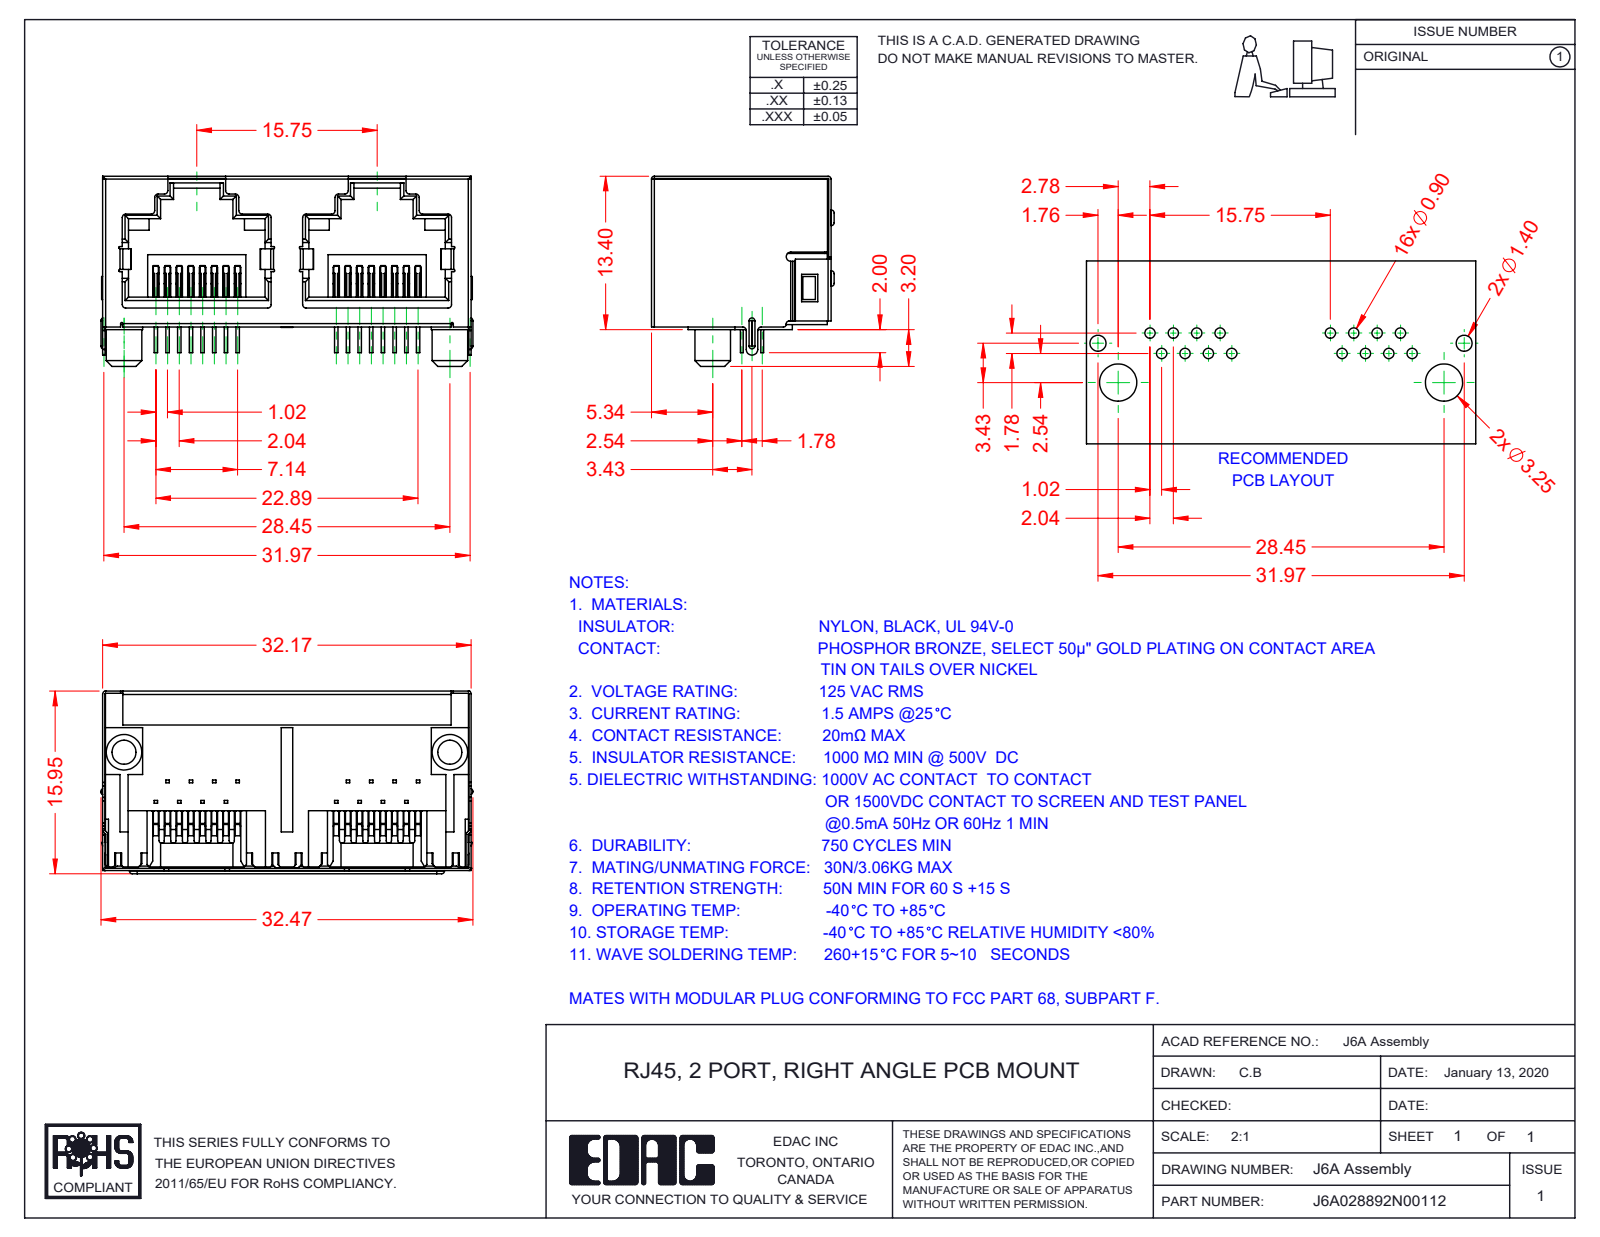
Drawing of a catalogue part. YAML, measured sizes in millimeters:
part_name: "6A Shield; 6A Insulator; J6A028892N00112; 6A Contacts"
step_written_by: "SolidWorks 2016 (CONFIG_CONTROL_DESIGN)"
units: millimeters
bodies: {solids: 18, faces: 1823, planar: 1380, cylindrical: 415, other: 28}
overall_size: [32.47, 16.6, 15.95]
volume: 2964
surface_area: 8172
round_bosses_or_shafts:
  - {diameter: 3.1, count: 2}
partial_cylinders:
  - {radius: 0.1, count: 44}
  - {radius: 0.3, count: 44}
  - {radius: 0.25, count: 23}
  - {radius: 0.2, count: 16}
  - {radius: 0.23, count: 14}
  - {radius: 0.21, count: 4}
  - {radius: 0.47, count: 4}
  - {radius: 0.68, count: 4}
face_to_face_distances: [15.75, 0.85, 31.97, 12.95, 12.7, 12.75, 15.47, 10.55, 2, 2.4]
